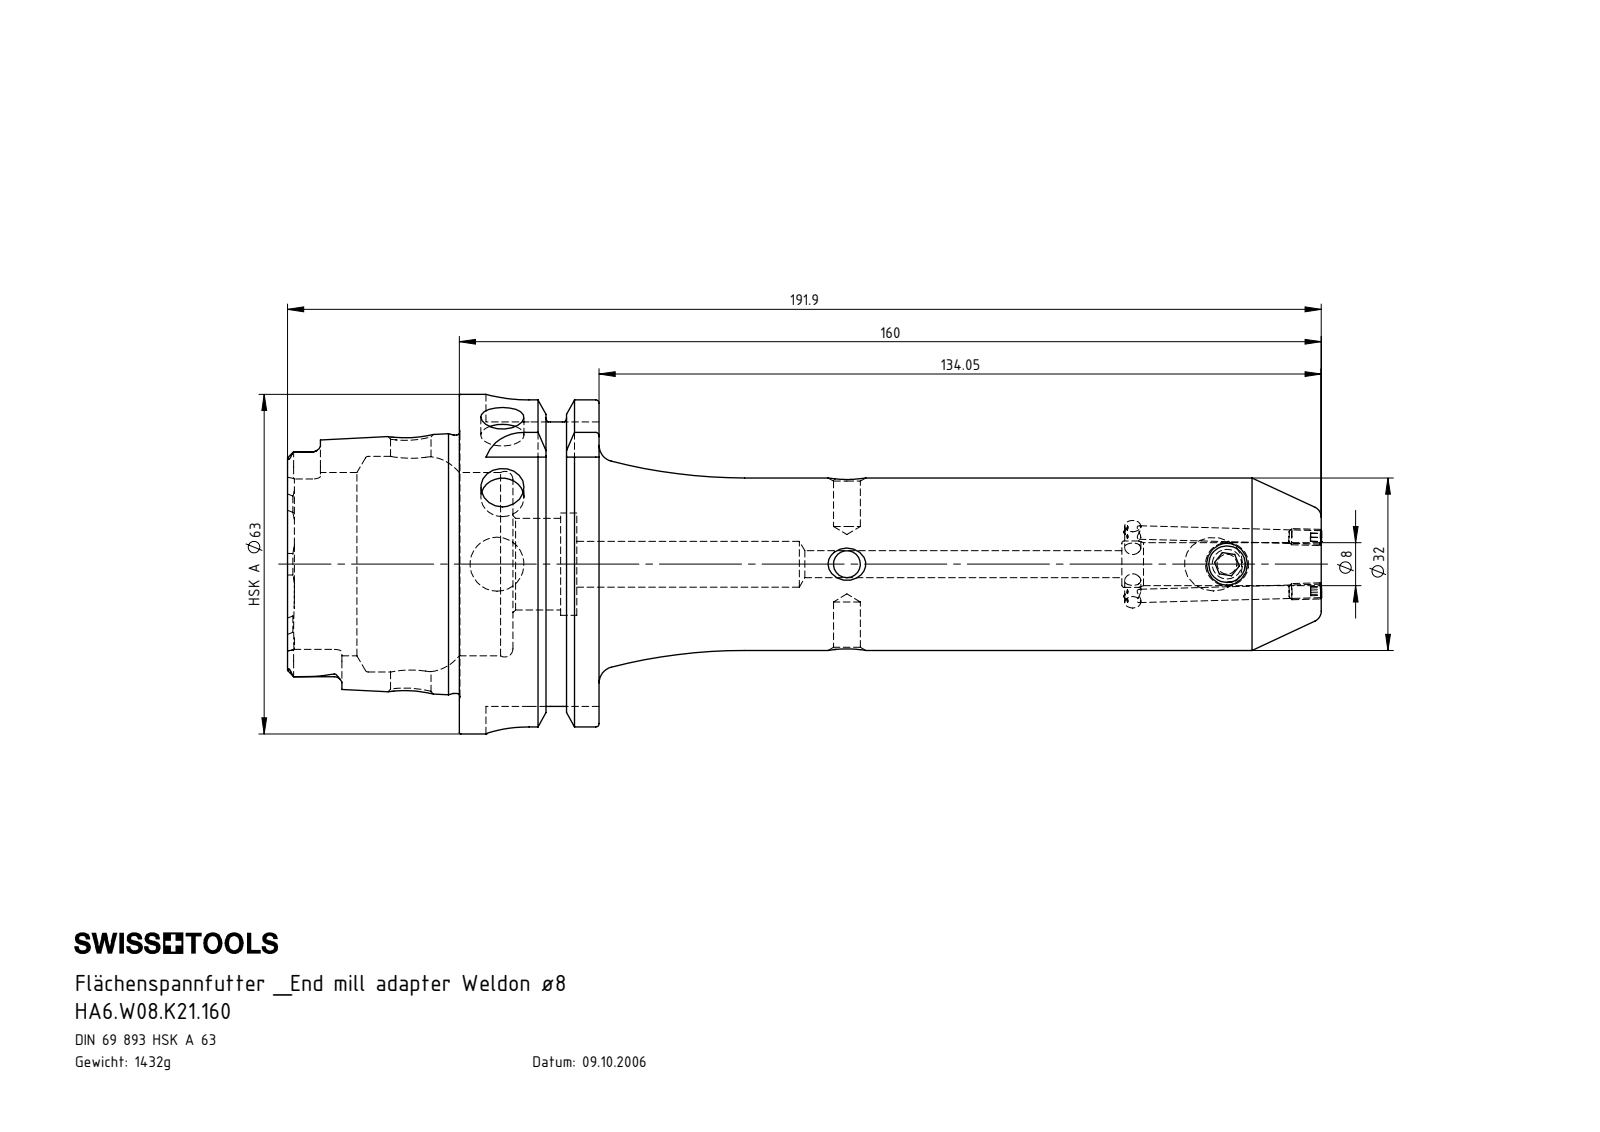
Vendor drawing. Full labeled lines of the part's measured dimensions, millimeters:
Part name (STEP PRODUCT): ERU-CJ2.001.006; W08-ER1.001.010; HA6-W08.K21.160_C_Fertigbearbeitung; HA6.W08.K21.160
STEP written by: SolidWorks 2012 (CONFIG_CONTROL_DESIGN)
Units: millimetres
Bodies: 4 solids, 292 faces (77 planar, 83 cylindrical, 132 other)
Overall size (bounding box): 191.98 × 63 × 63
Volume: 182 461 mm³ · Surface area: 39 874 mm²
Round holes (diameter × count): ⌀5 ×3, ⌀8 ×3, ⌀2.5 ×2, ⌀3 ×1, ⌀6.8 ×1, ⌀7.5 ×1, ⌀8.5 ×1, ⌀8.6 ×1, ⌀10 ×1, ⌀17 ×1, ⌀19 ×1, ⌀34 ×1
Round bosses / shafts (diameter × count): ⌀3 ×2, ⌀63 ×1, ⌀54.95 ×1, ⌀47.94 ×1, ⌀32 ×1, ⌀8 ×1
Partial cylindrical surfaces — rounded edges, fillets, slot ends (radius × count): R1.4 ×6, R2.88 ×4, R8 ×4
Main face-to-face distances: 25.95, 16, 9.95, 31.9, 41.85, 57.85, 52.8, 21.8, 11.85, 53.7
Hole centre spacings: 64.95, 70.55, 80.95, 135.5
